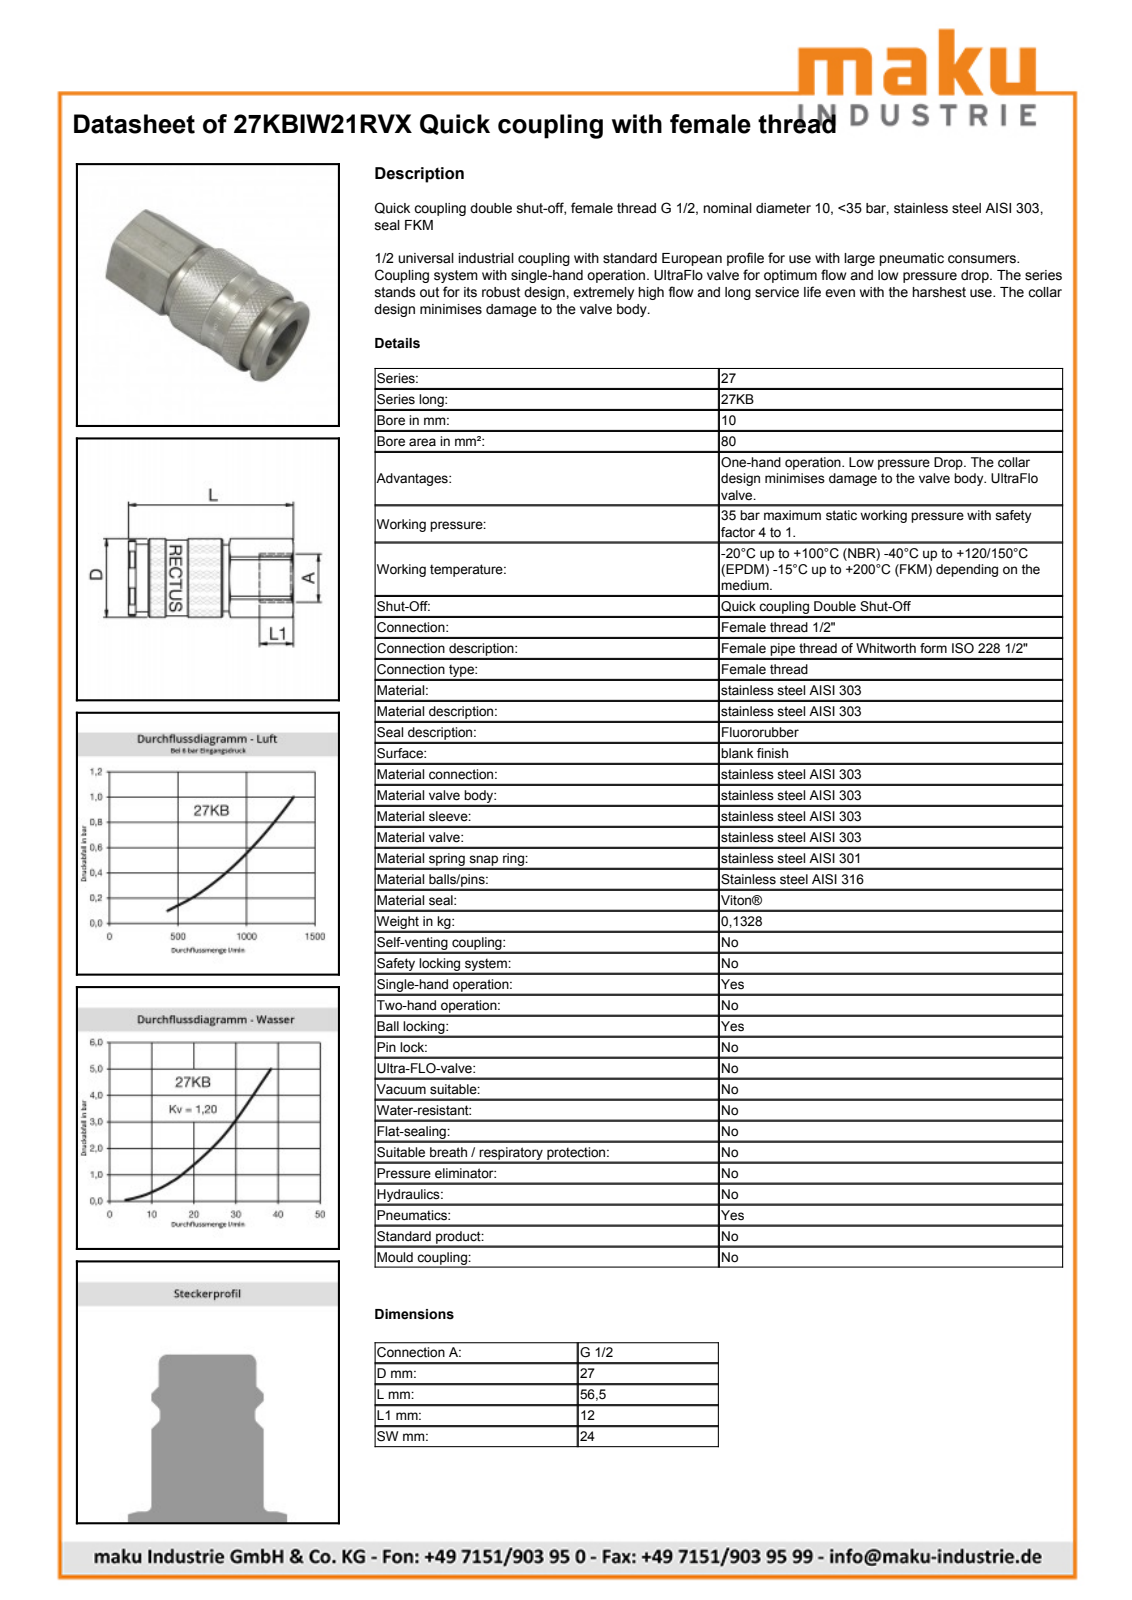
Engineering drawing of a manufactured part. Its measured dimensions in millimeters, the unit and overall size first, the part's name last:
Units: millimetres
Overall size (bounding box): 56.5 × 27.15 × 27.15
Round holes (diameter × count): ⌀20.3 ×1, ⌀20.95 ×1, ⌀20.96 ×1, ⌀23.35 ×1, ⌀23.55 ×1
Round bosses / shafts (diameter × count): ⌀27.15 ×1, ⌀26 ×1, ⌀23.1 ×1, ⌀22.75 ×1, ⌀20 ×1
Partial cylindrical surfaces — rounded edges, fillets, slot ends (radius × count): R9.76 ×1, R12.9 ×1, R13.53 ×1
Main face-to-face distances: 24, 31.75, 6.25, 25.5, 25, 2.5, 3.75, 29.25, 16.75, 14.25
Volume: 23 808 mm³ · Surface area: 10 630 mm²
Bodies: 2 solids, 822 faces (319 planar, 87 cylindrical, 416 other)
Part name (STEP PRODUCT): D105216
STEP written by: Autodesk Inventor 2013 (AUTOMOTIVE_DESIGN)
